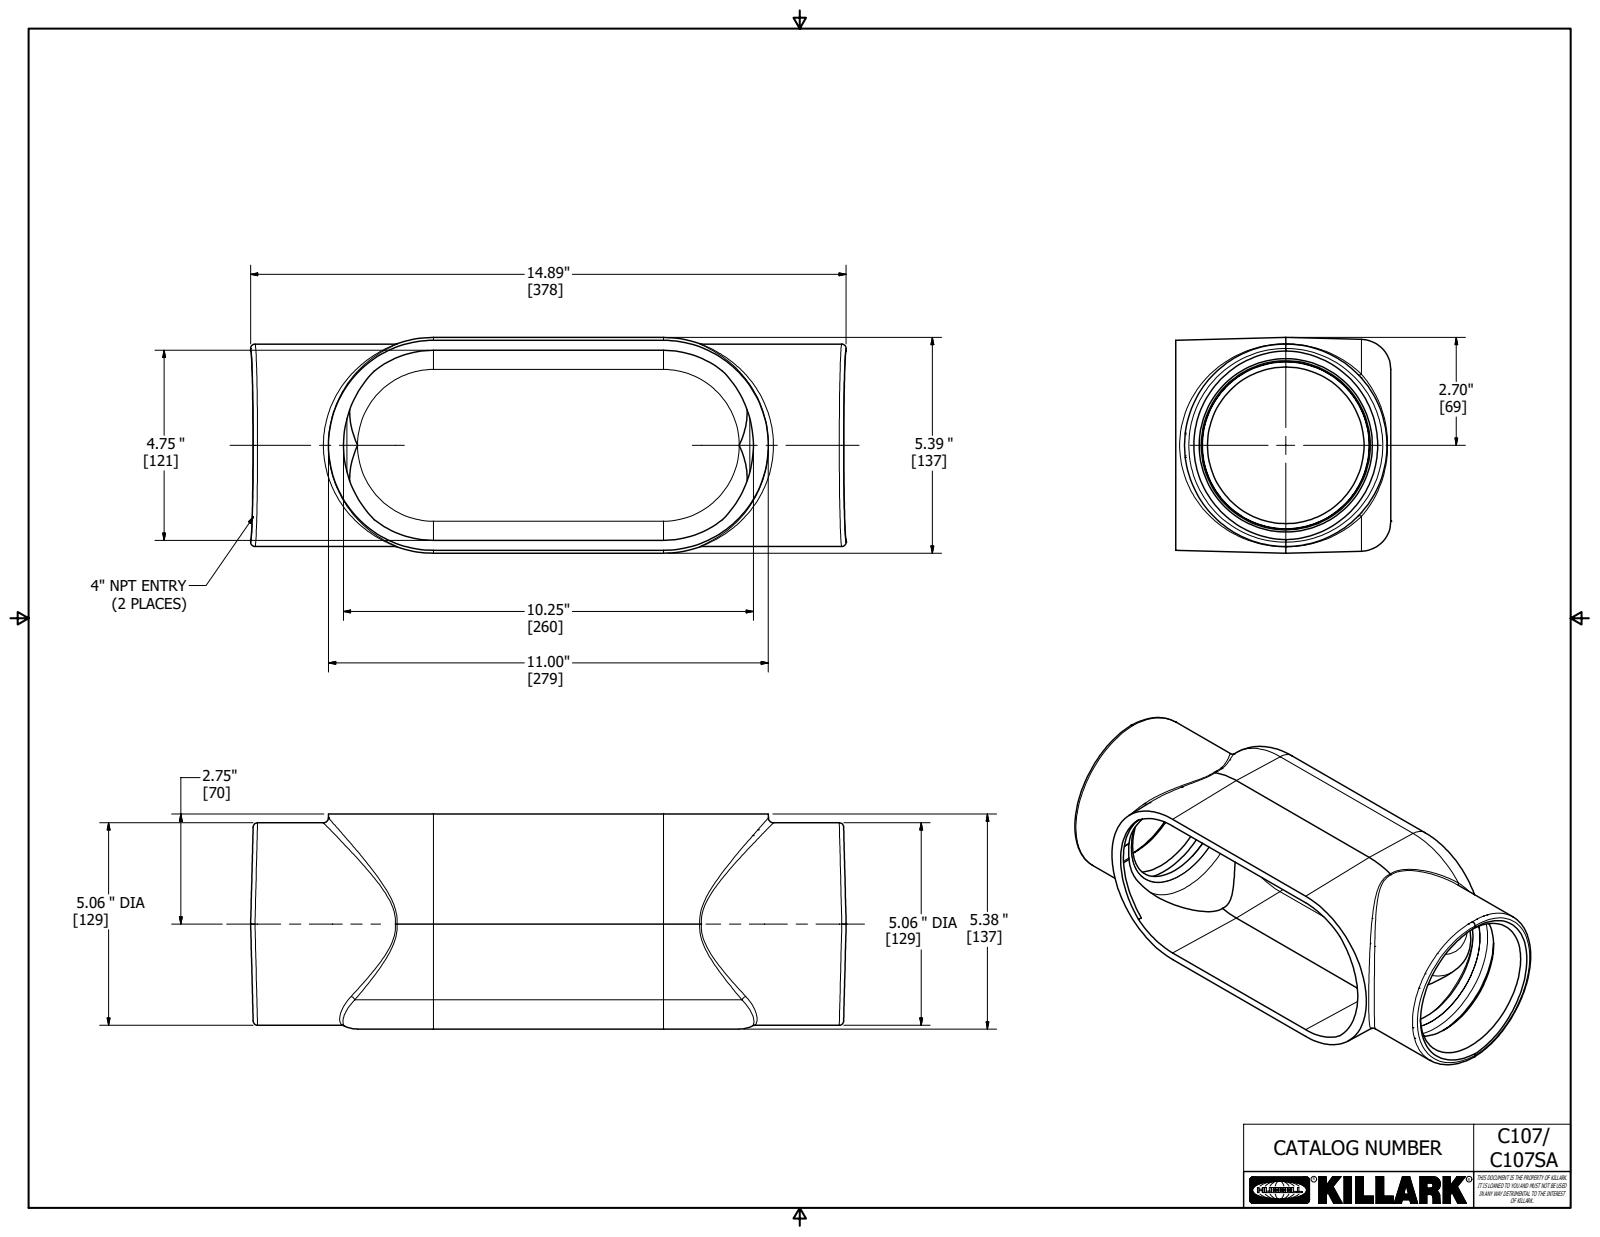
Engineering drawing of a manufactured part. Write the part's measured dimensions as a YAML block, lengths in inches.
part_name: "17737"
step_written_by: "Autodesk Inventor 2018 (AUTOMOTIVE_DESIGN)"
units: inches
bodies: {solids: 1, faces: 92, planar: 28, cylindrical: 18, other: 46}
overall_size: [14.894, 5.394, 5.375]
volume: 62.09
surface_area: 475
round_holes:
  - {diameter: 4.511, count: 1}
  - {diameter: 4.75, count: 1}
round_bosses_or_shafts:
  - {diameter: 5.062, count: 1}
partial_cylinders:
  - {radius: 0.05, count: 4}
  - {radius: 0.125, count: 4}
  - {radius: 0.5, count: 2}
  - {radius: 0.75, count: 2}
face_to_face_distances: [0.25, 5.144, 5.394, 4.894, 5.375, 5.125, 0.031, 0.219, 5.344, 14.894]
